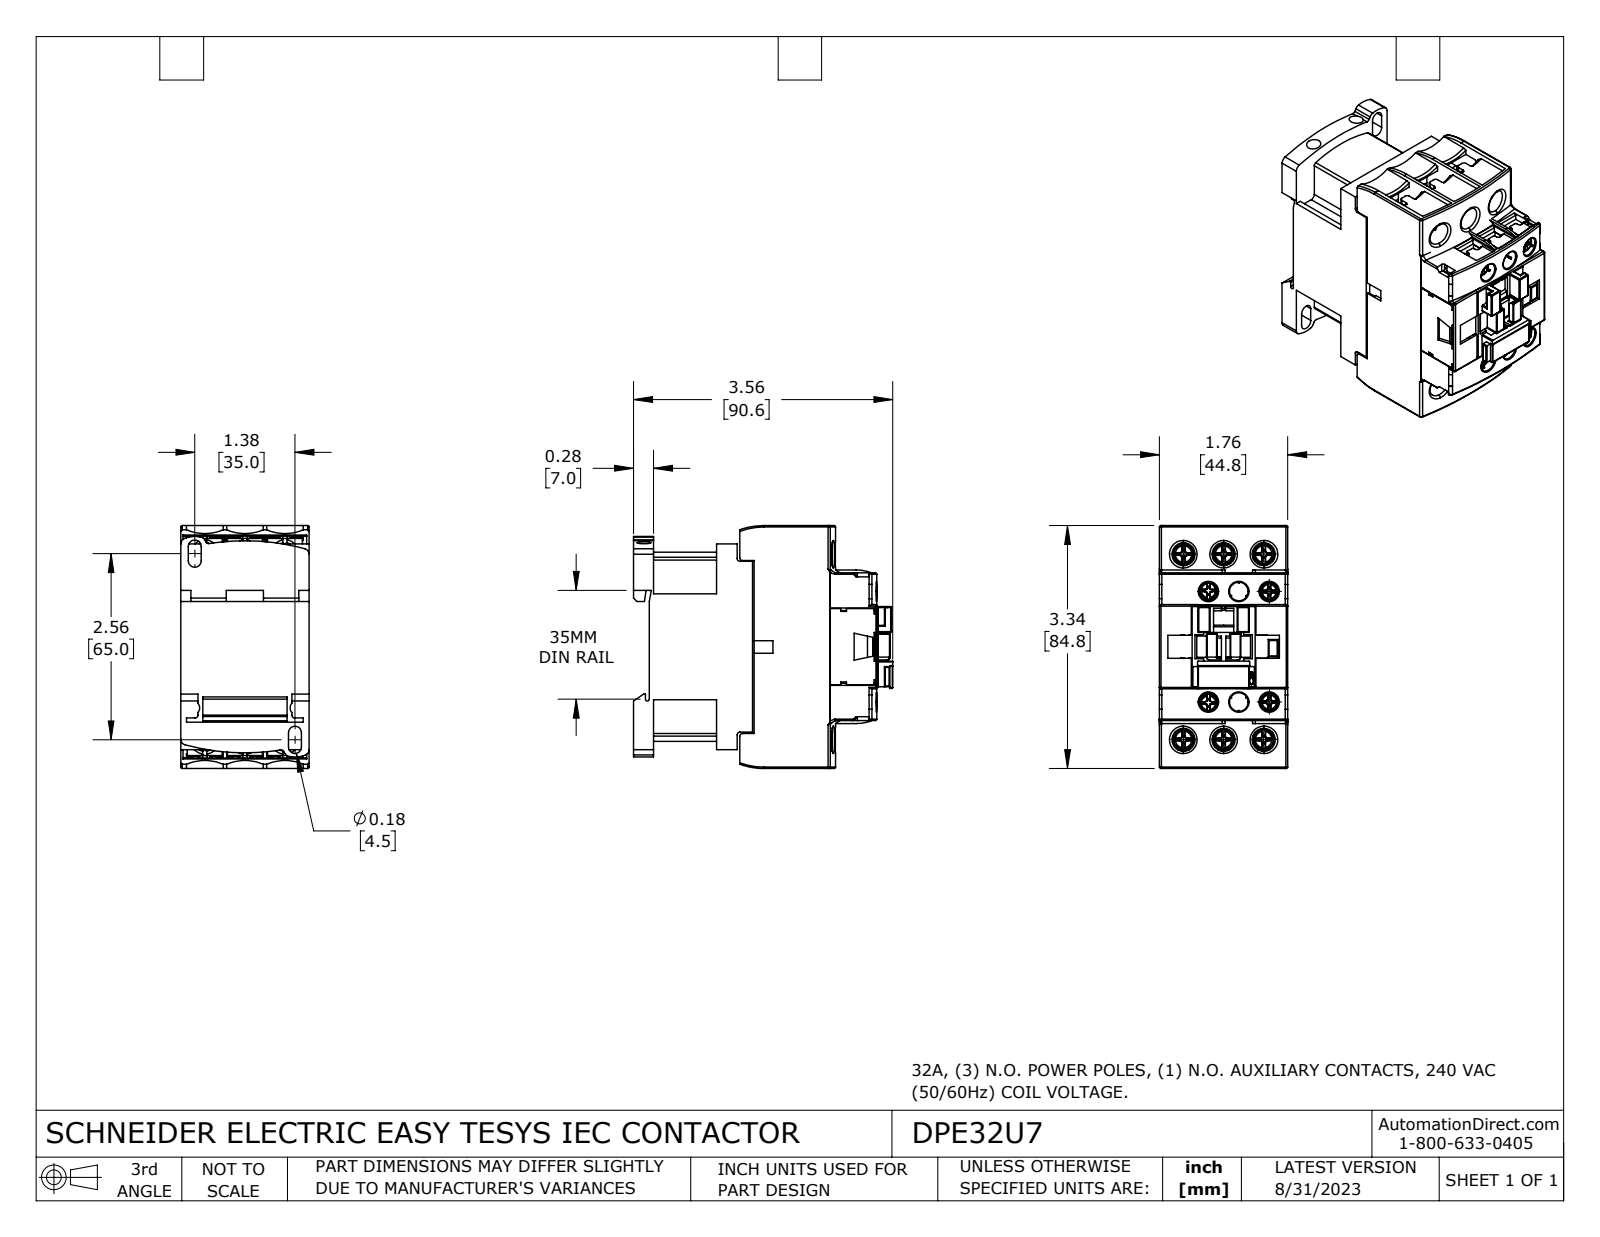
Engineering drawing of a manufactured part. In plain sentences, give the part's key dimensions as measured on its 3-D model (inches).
The part is named "DPE32U7". Its 3-D file was written by "SolidWorks 2021 (CONFIG_CONTROL_DESIGN)". It is 16 solids with 2674 faces: 1724 planar, 584 cylindrical and 366 other. Overall it measures 3.565 by 3.339 by 1.764 inches. Its volume is 12.56 cubic inches and its surface area 100.4 square inches. Round holes: 6 of diameter 0.256, 6 of diameter 0.315, 2 of diameter 0.197. Round bosses or shafts: 8 of diameter 0.157, 6 of diameter 0.126, 4 of diameter 0.138, 4 of diameter 0.134, 4 of diameter 0.108, 3 of diameter 0.394. Partial cylindrical surfaces (rounded edges, fillets, slot ends): 58 of radius 0.012, 36 of radius 0.006, 36 of radius 0.039, 34 of radius 0.02, 18 of radius 0.63, 17 of radius 0.008, 9 of radius 0.079, 8 of radius 0.031. The main face-to-face distances are 1.764, 0.551, 0.022, 0.059, 1.089, 1.067, 0.047, 0.031, 1.382, 1.419. The hole center spacings are 0.417, 0.551, 1.576, 2.61, 1.52, 2.551, 0.553, 0.56.
